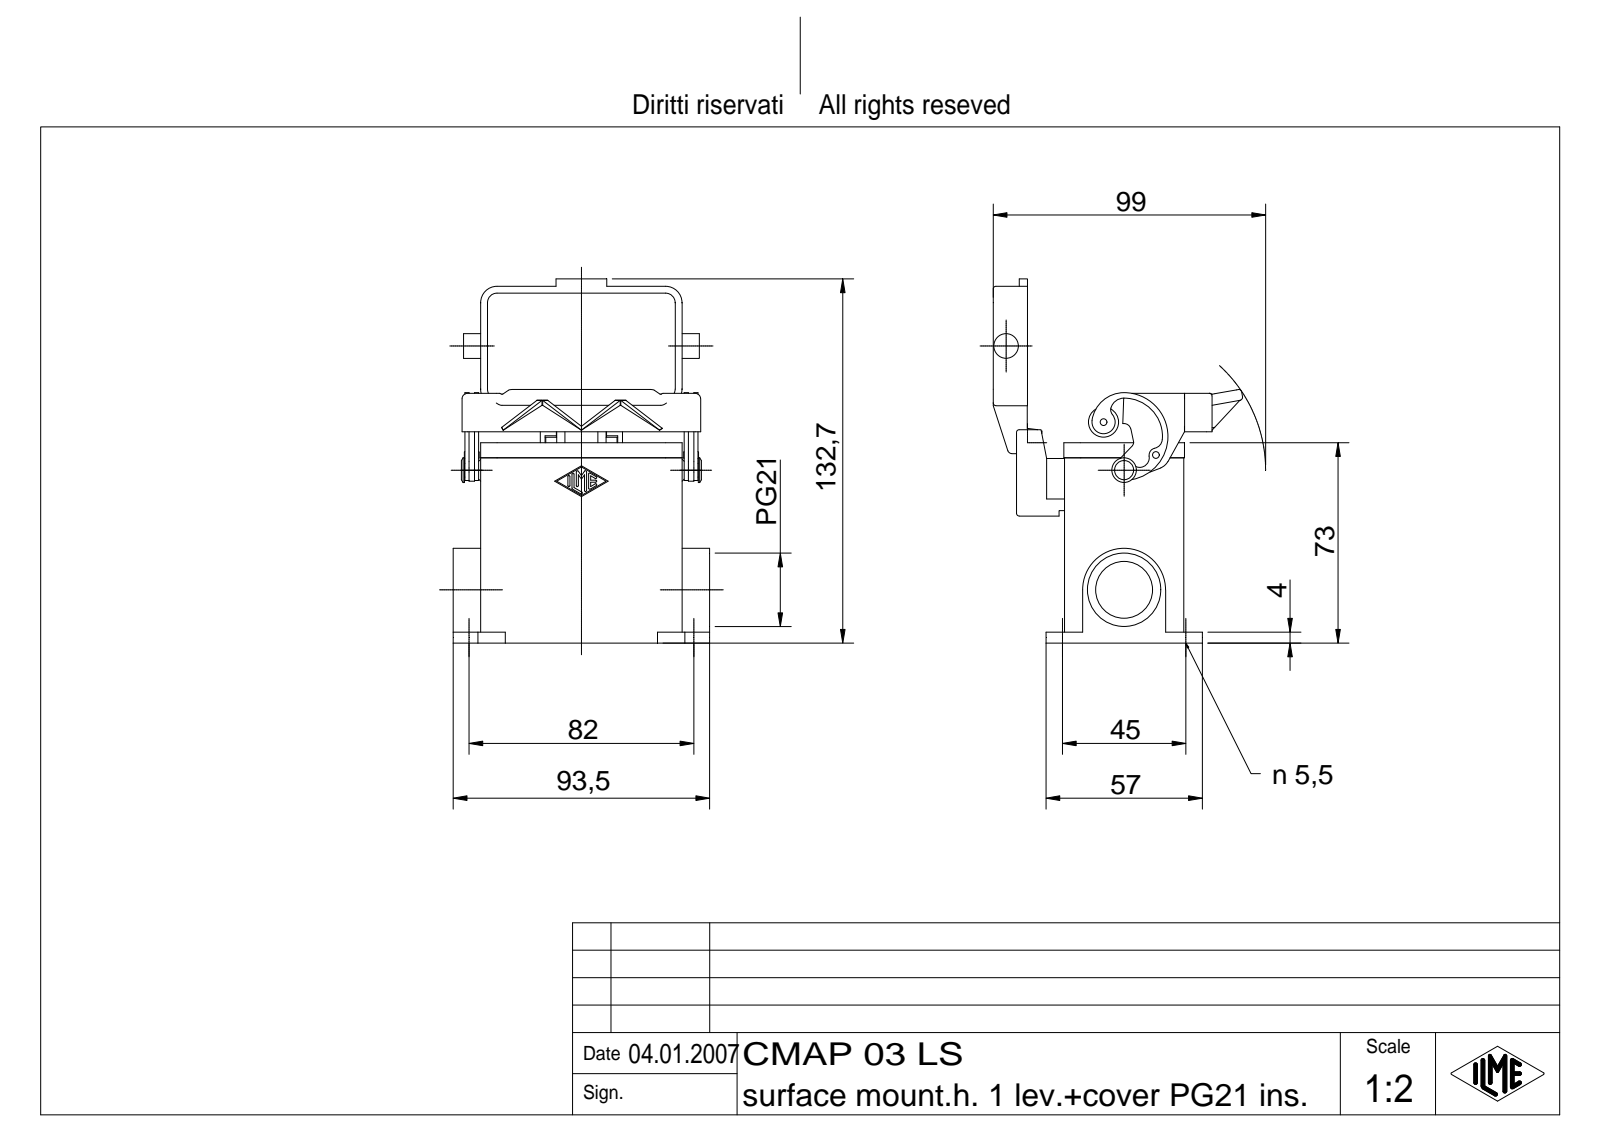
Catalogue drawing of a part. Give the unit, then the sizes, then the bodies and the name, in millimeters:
Units: millimetres
Overall size (bounding box): 132.7 × 93.5 × 90.95
Round holes (diameter × count): ⌀5.5 ×4, ⌀2 ×1, ⌀4 ×1, ⌀20.78 ×1, ⌀26.78 ×1
Round bosses / shafts (diameter × count): ⌀9 ×2, ⌀5 ×2, ⌀11 ×1, ⌀7 ×1, ⌀4 ×1, ⌀3 ×1, ⌀2.5 ×1
Partial cylindrical surfaces — rounded edges, fillets, slot ends (radius × count): R1 ×18, R0.38 ×14, R2 ×12, R6 ×12, R1.5 ×6, R3.5 ×6, R3 ×4, R0.5 ×3
Main face-to-face distances: 3, 40.5, 4, 43.5, 26, 37.5, 66.5, 11.75, 61.75, 69.5
Hole centre spacings: 45, 82, 93.54, 50.46
Volume: 131 452 mm³ · Surface area: 71 290 mm²
Bodies: 6 solids, 592 faces (252 planar, 180 cylindrical, 160 other)
Part name (STEP PRODUCT): CMAP 03 LS
STEP written by: Autodesk Inventor 7 (AUTOMOTIVE_DESIGN)
